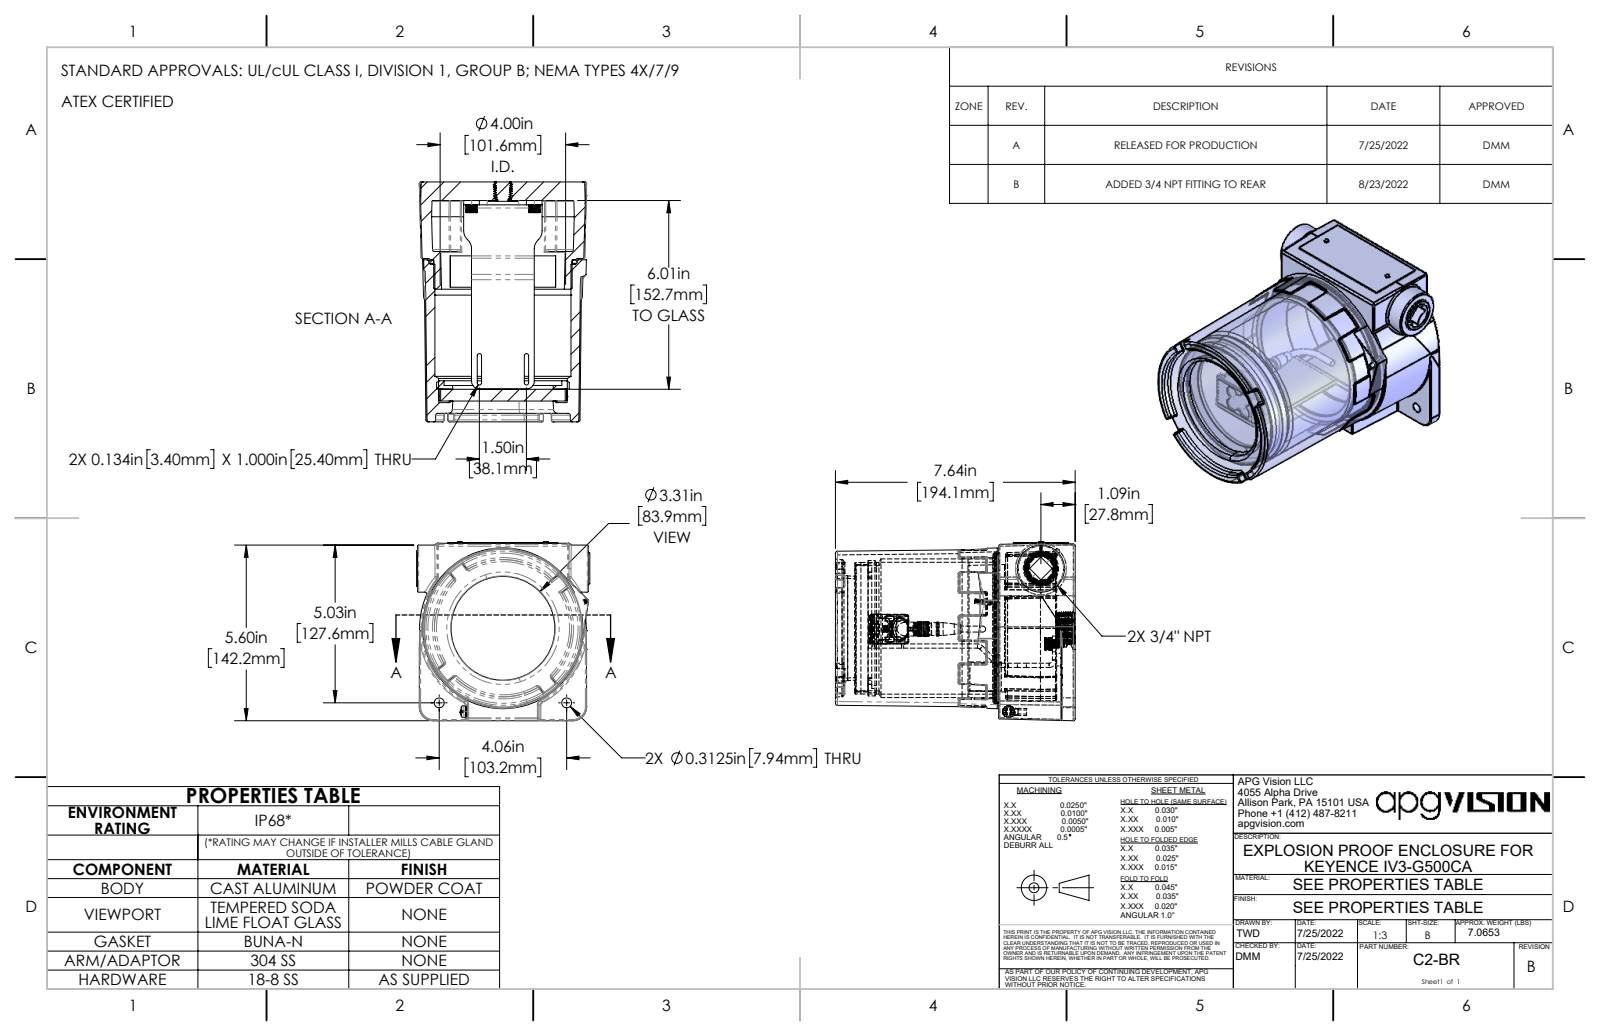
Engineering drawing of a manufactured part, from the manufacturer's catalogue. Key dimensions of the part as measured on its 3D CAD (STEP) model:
Part name (STEP PRODUCT): 4638K515_4638K515; 92196A535_92196A535; 91292A033_91292A033; C2-BR (+3 more)
STEP written by: SolidWorks 2021 (CONFIG_CONTROL_DESIGN)
Units: inches
Bodies: 26 solids, 1893 faces (501 planar, 448 cylindrical, 944 other)
Overall size (bounding box): 9.694 × 7.735 × 7.229
Volume: 67.15 in³ · Surface area: 475.3 in²
Round holes (diameter × count): ⌀0.067 ×2, ⌀0.093 ×2, ⌀0.094 ×2, ⌀0.118 ×2, ⌀0.145 ×2, ⌀0.188 ×2, ⌀0.201 ×2, ⌀0.266 ×2, ⌀0.313 ×2, ⌀0.4 ×2, ⌀0.107 ×1, ⌀0.129 ×1
Round bosses / shafts (diameter × count): ⌀0.25 ×2, ⌀0.217 ×2, ⌀0.19 ×2, ⌀0.185 ×2, ⌀0.118 ×2, ⌀0.073 ×2, ⌀4.77 ×1, ⌀4.492 ×1
Partial cylindrical surfaces — rounded edges, fillets, slot ends (radius × count): R0.031 ×19, R0.031 ×11, R0.25 ×6, R0.063 ×5, R0.063 ×5, R0.067 ×4, R0.394 ×4, R0.025 ×3
Main face-to-face distances: 0.594, 6.982, 6.388, 6.607, 6.013, 0.375, 0.135, 0.615, 0.02, 3.362
Hole centre spacings: 1.118, 0.707, 1.581, 1.781, 2.058, 2.14, 2.88, 3.125
